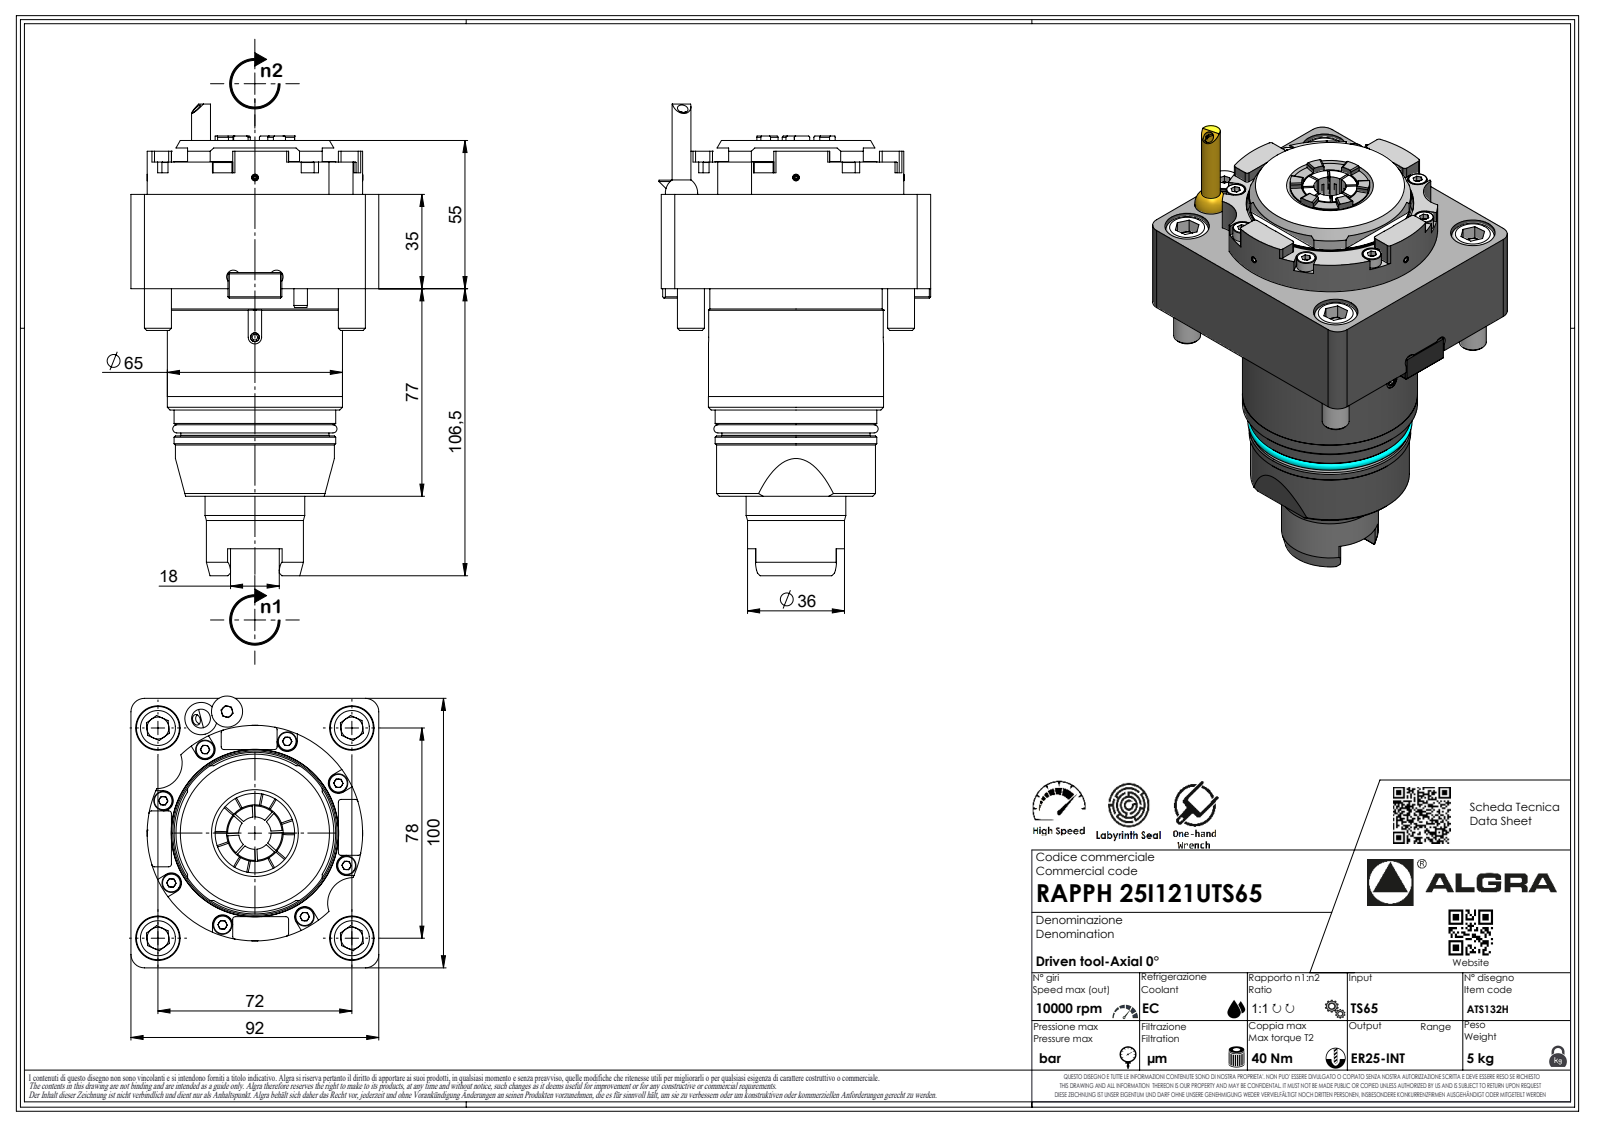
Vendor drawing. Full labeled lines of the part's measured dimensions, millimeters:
Part name (STEP PRODUCT): RAPPH25I121UT65
STEP written by: SolidWorks 2023 (AUTOMOTIVE_DESIGN)
Units: millimetres
Bodies: 3 solids, 496 faces (323 planar, 77 cylindrical, 96 other)
Overall size (bounding box): 175 × 100 × 92
Volume: 669 176 mm³ · Surface area: 59 525 mm²
Round holes (diameter × count): ⌀2.1 ×1, ⌀4 ×1
Round bosses / shafts (diameter × count): ⌀10 ×4, ⌀80 ×1, ⌀65 ×1, ⌀64.99 ×1, ⌀64 ×1, ⌀60 ×1, ⌀59 ×1, ⌀55 ×1
Partial cylindrical surfaces — rounded edges, fillets, slot ends (radius × count): R1 ×16, R0.33 ×7, R0.52 ×7, R3.7 ×7, R0.75 ×4, R5 ×4, R9.5 ×2, R0.21 ×1
Main face-to-face distances: 35, 92, 100, 20, 55, 47, 12, 77, 4, 8
